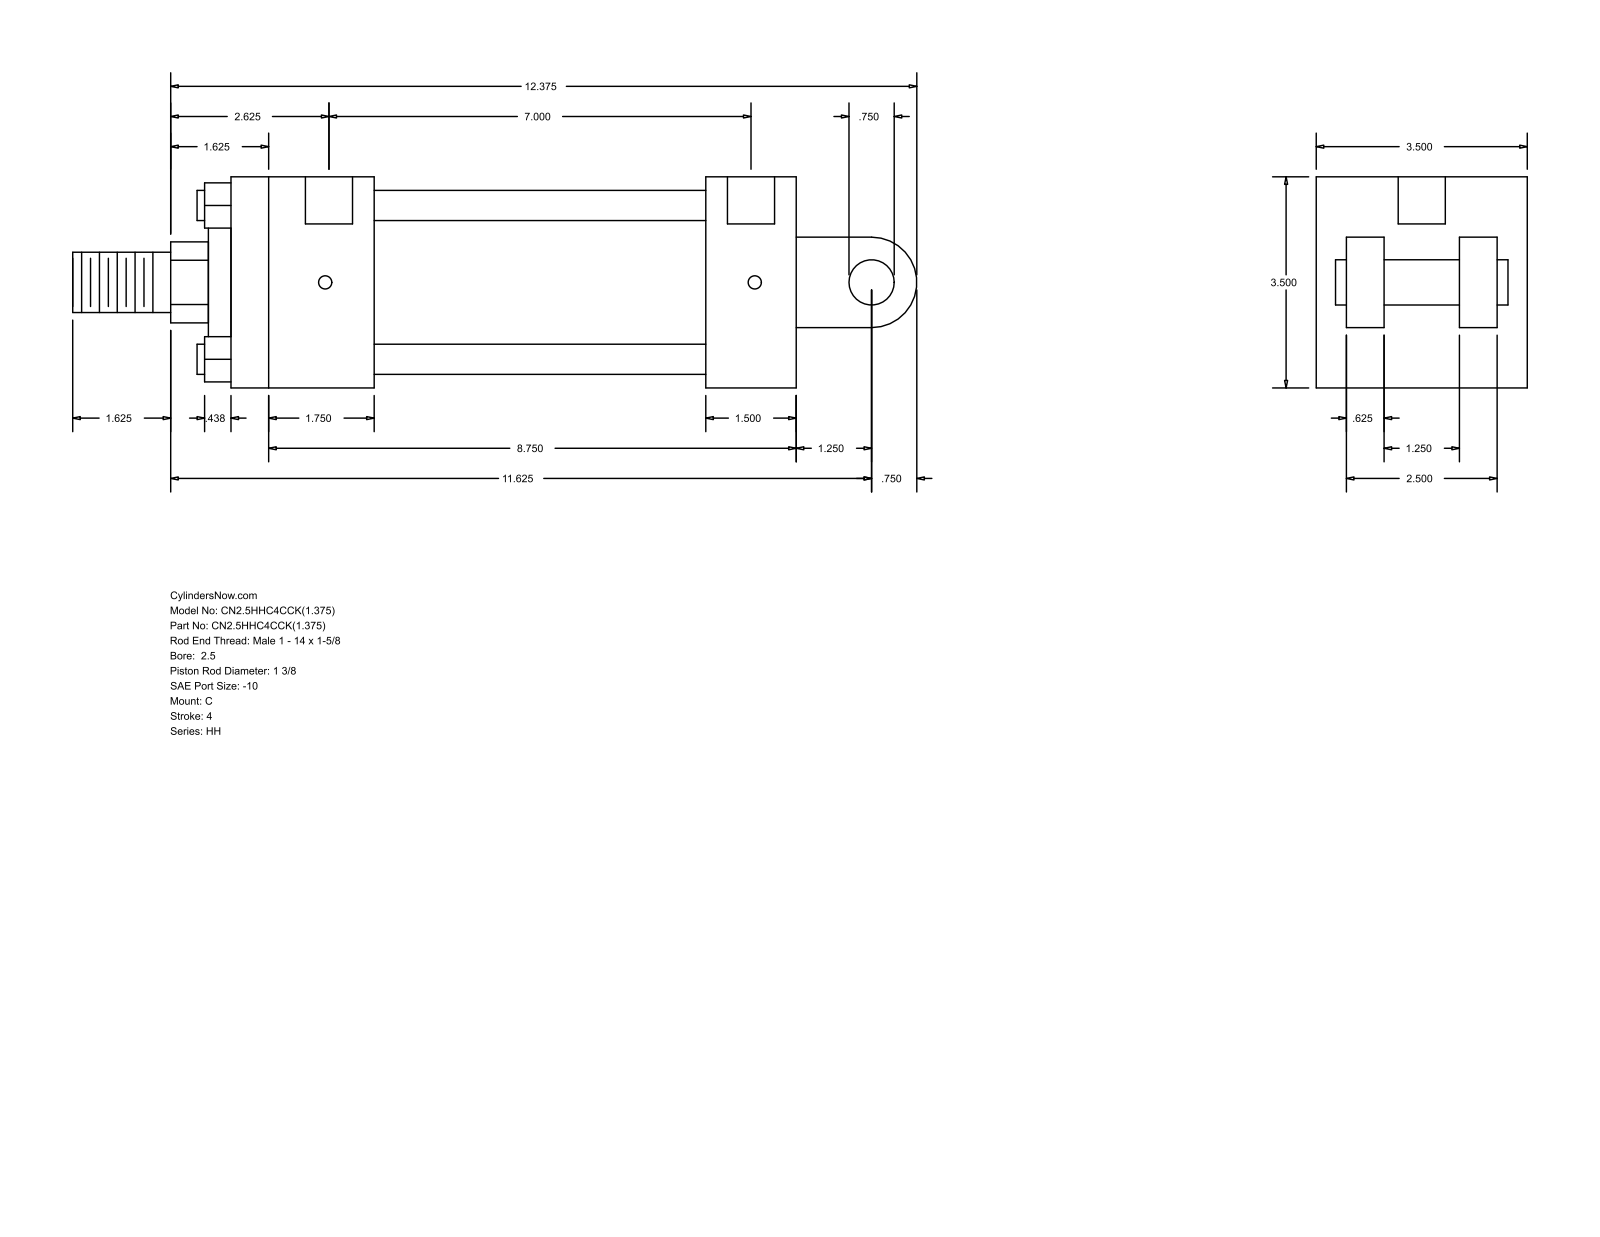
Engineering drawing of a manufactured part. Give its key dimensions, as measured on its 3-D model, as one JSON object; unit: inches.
{"part_name": "HH_C__0250_1.375", "step_written_by": "GSSL Pune (CONFIG_CONTROL_DESIGN)", "units": "inches", "bodies": {"solids": 0, "faces": 99, "planar": 70, "cylindrical": 29, "other": 0}, "overall_size": [14, 3.5, 3.5], "round_holes": [[0.219, 4], [0.781, 2]], "round_bosses_or_shafts": [[0.5, 4], [2.875, 1], [2, 1], [1.375, 1], [1, 1], [0.75, 1]], "partial_cylinders_radius": [[0.672, 1], [0.75, 1]], "face_to_face_distances": [3.5, 9.375, 2.5, 0.5, 7.875, 1.5, 2.375, 5.5, 7, 3], "hole_center_spacings": [7.125, 0.062, 0.063, 7, 7.062, 7.063]}
